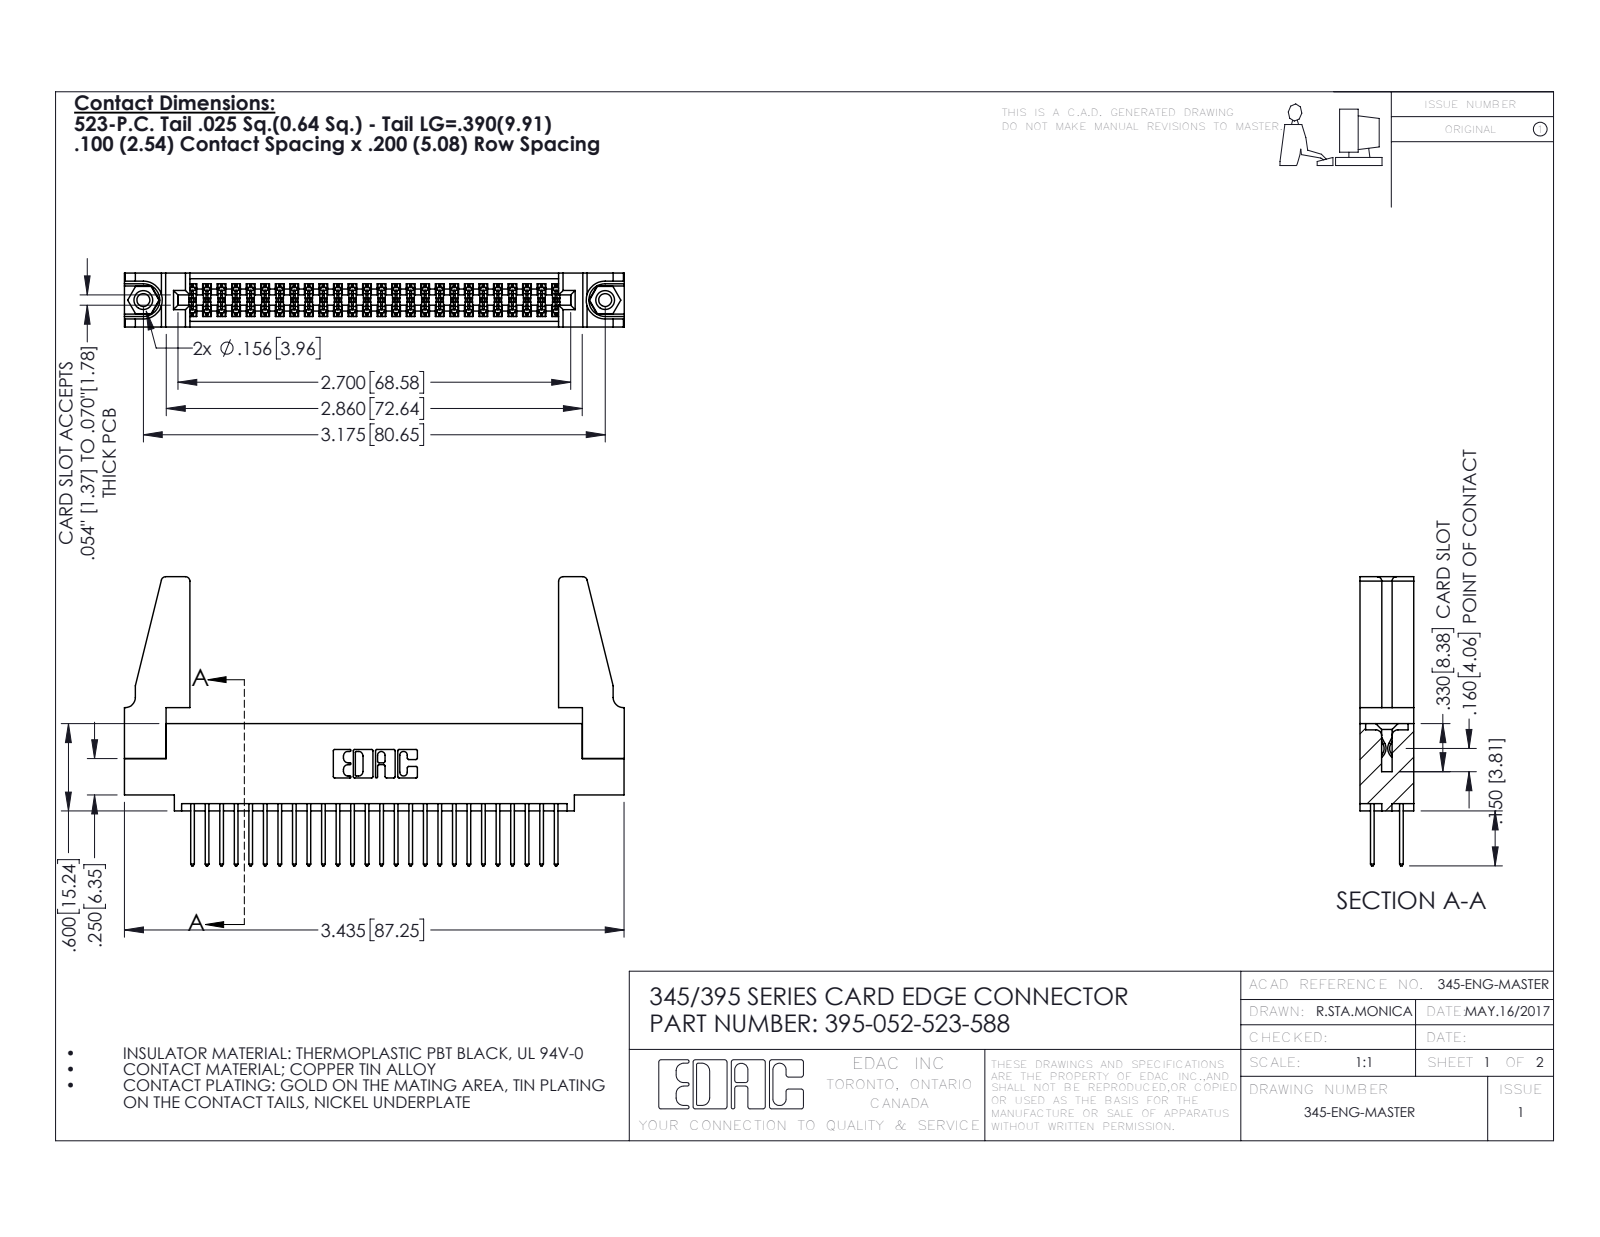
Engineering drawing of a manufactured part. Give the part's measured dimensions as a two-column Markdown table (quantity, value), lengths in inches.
| quantity | value |
| --- | --- |
| part name | 345-292-001_345-293-123; 395-052-523-588; 345-220-078_345-220-088; 345-250-001_345-250-001-102 (+1 more) |
| STEP written by | SolidWorks 2016 (CONFIG_CONTROL_DESIGN) |
| units | inches |
| bodies | 57 solids, 2854 faces (1872 planar, 966 cylindrical, 16 other) |
| overall size | 3.436 × 1.987 × 0.37 |
| volume | 0.709 in³ |
| surface area | 24.4 in² |
| round holes (diameter × count) | 0.089 × 2, 0.125 × 2, 0.156 × 2, 0.064 × 1 |
| round bosses / shafts (diameter × count) | 0.155 × 2 |
| partial cylindrical surfaces (radius × count) | 0.006 × 78, 0.01 × 52, 0.01 × 22, 0.03 × 8, 0.007 × 6, 0.031 × 6, 0.026 × 3, 0.014 × 2 |
| main face-to-face distances | 0.072, 0.298, 0.37, 0.2, 0.098, 0.272, 0.025, 0.225, 0.175, 0.149 |
| hole center spacings | 0.27, 2.94, 3.175 |
